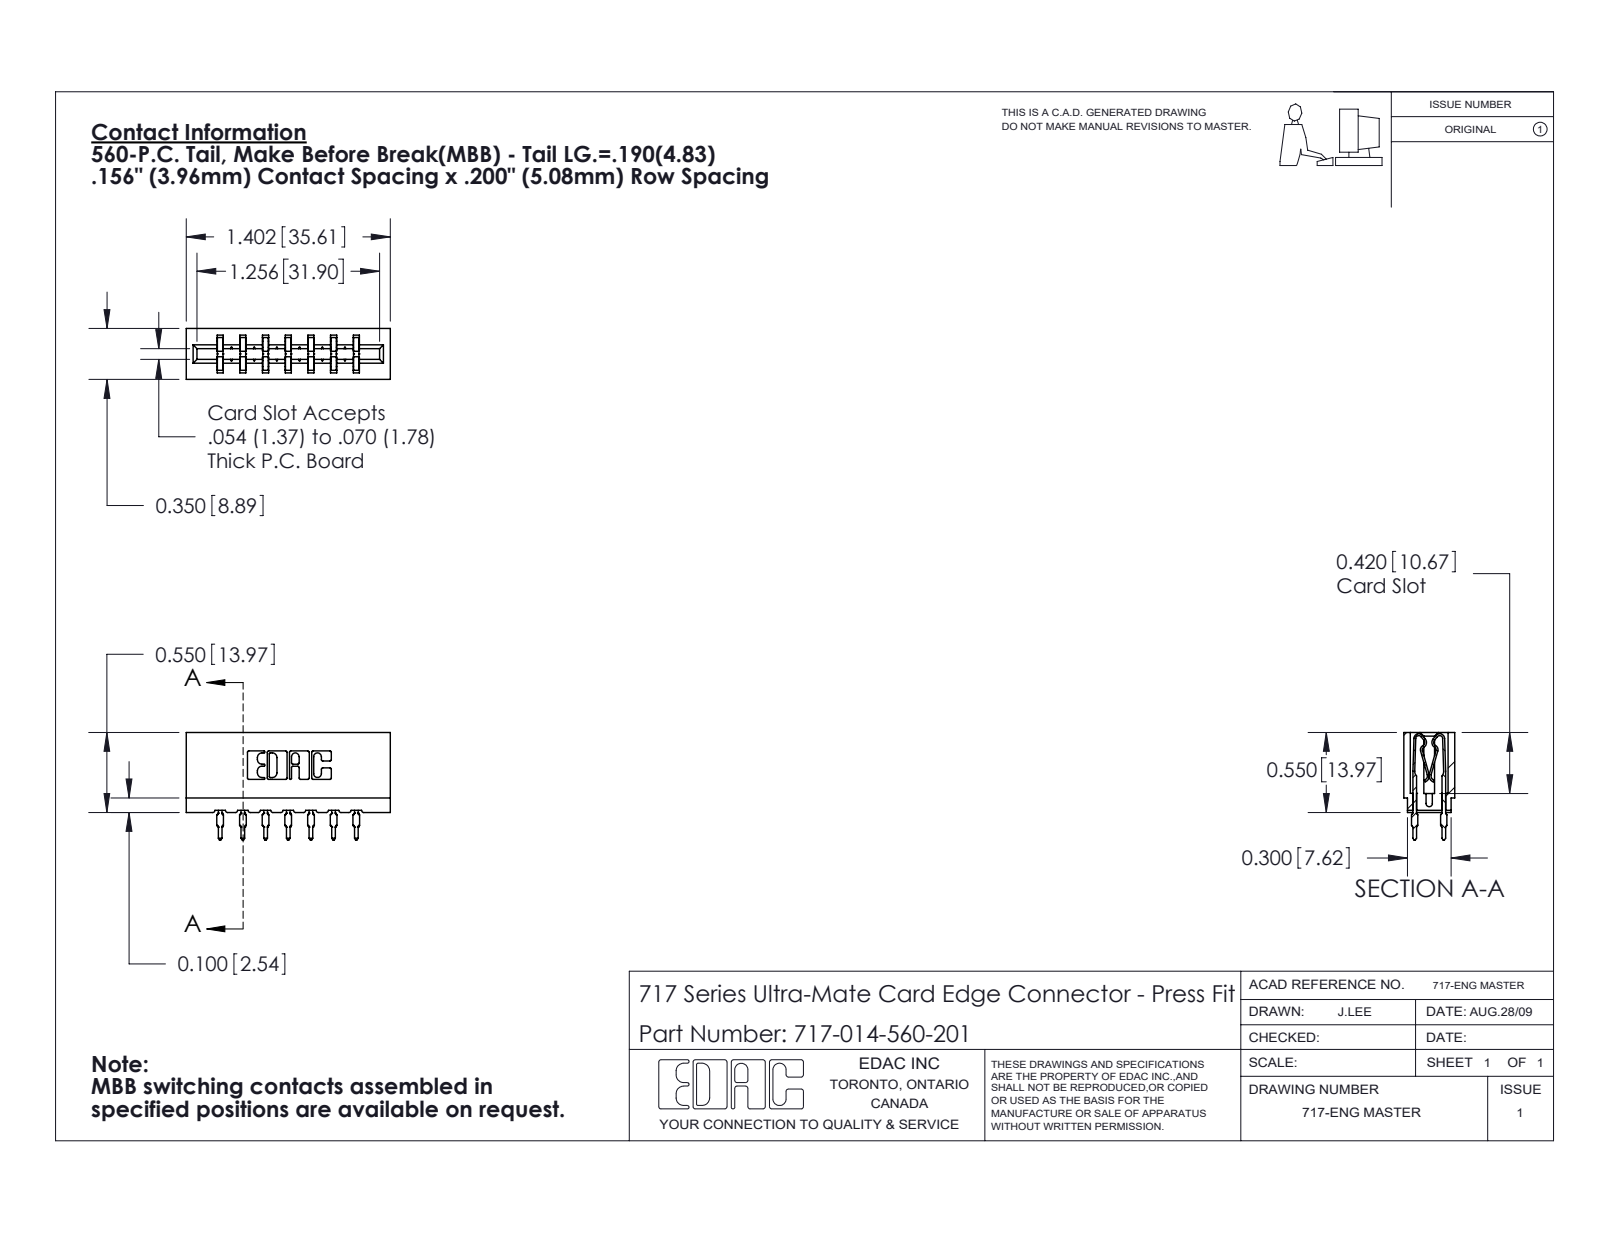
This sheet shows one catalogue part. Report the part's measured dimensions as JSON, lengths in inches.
{"part_name": "745-292-001_560; 717 Part_Insulator Option - 06; 717-014-560-201", "step_written_by": "SolidWorks 2020 (CONFIG_CONTROL_DESIGN)", "units": "inches", "bodies": {"solids": 15, "faces": 1480, "planar": 775, "cylindrical": 341, "other": 364}, "overall_size": [1.402, 0.739, 0.35], "volume_in3": 0.2, "surface_area_in2": 7.436, "partial_cylinders_radius": [[0.021, 28], [0.01, 22], [0.015, 14], [0.005, 8], [0.011, 8], [0.007, 6], [0.031, 6], [0.026, 3]], "face_to_face_distances": [0.212, 0.156, 0.138, 0.35, 0.198, 0.312, 0.468, 0.624, 0.042, 0.27]}
